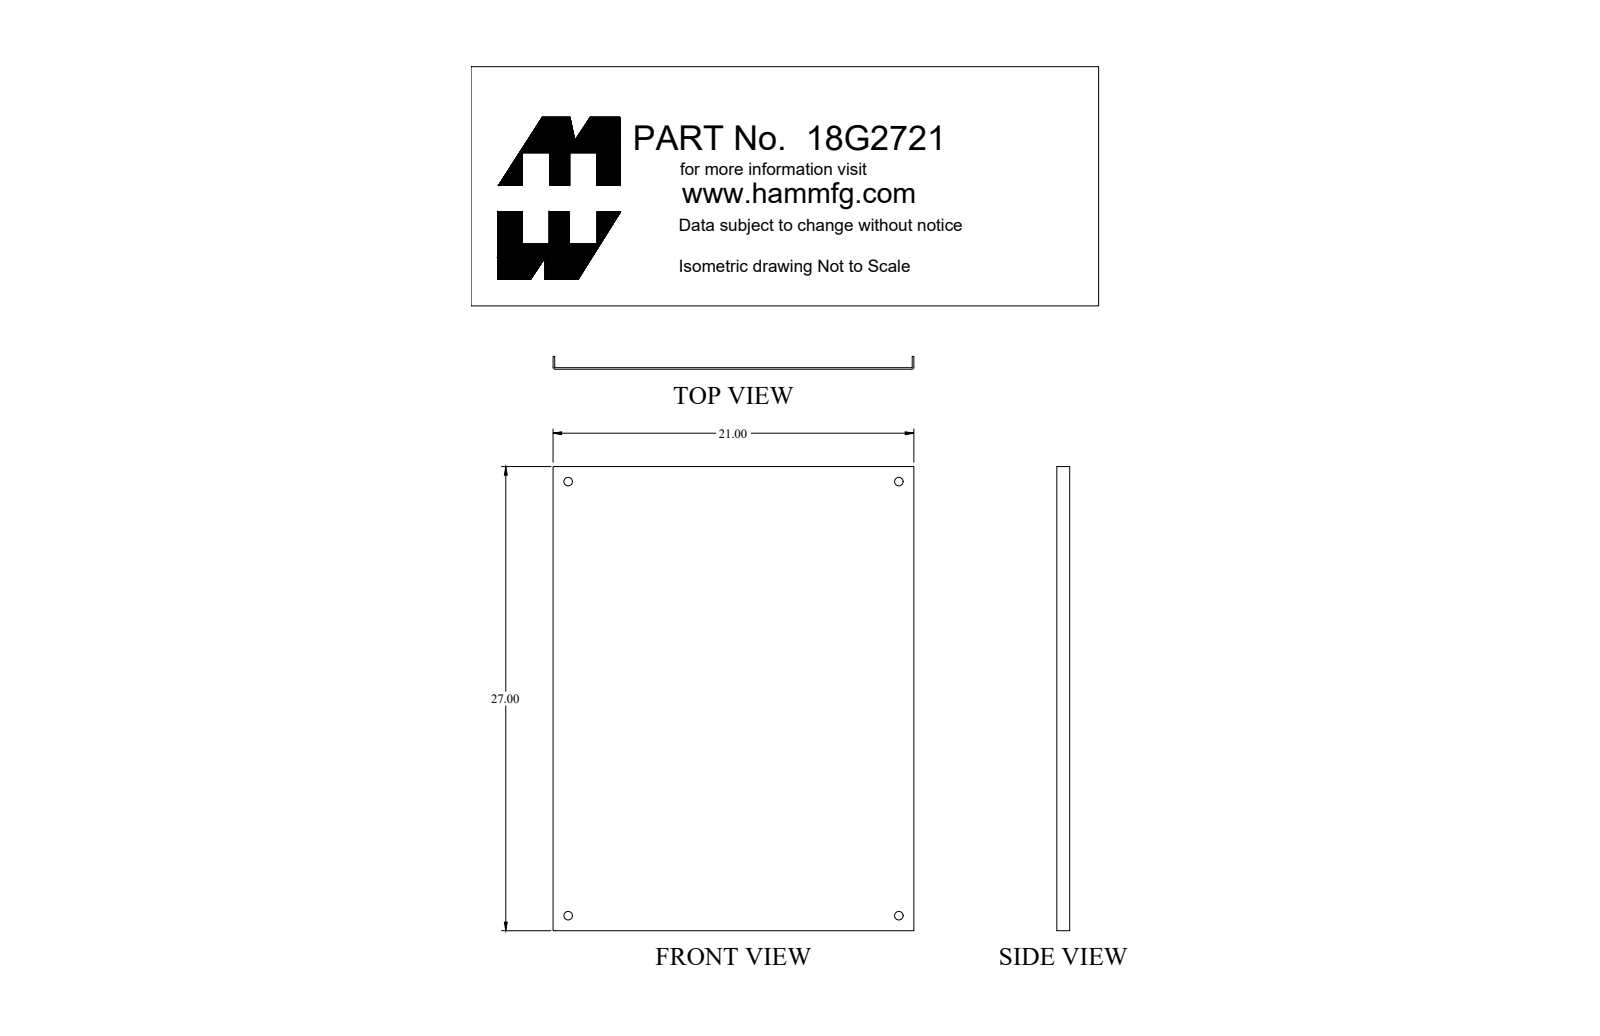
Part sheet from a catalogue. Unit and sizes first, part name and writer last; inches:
Units: inches
Overall size (bounding box): 27 × 21 × 0.75
Round holes (diameter × count): ⌀0.5 ×4
Partial cylindrical surfaces — rounded edges, fillets, slot ends (radius × count): R0.03 ×2, R0.125 ×2
Main face-to-face distances: 0.095, 20.905, 21, 20.81, 0.75, 0.655, 27
Hole centre spacings: 19.25, 25.25, 31.75
Volume: 56.98 in³ · Surface area: 1 210 in²
Bodies: 1 solid, 18 faces (10 planar, 8 cylindrical, 0 other)
Part name (STEP PRODUCT): 18G2721
STEP written by: SolidWorks 2018 (AUTOMOTIVE_DESIGN)
